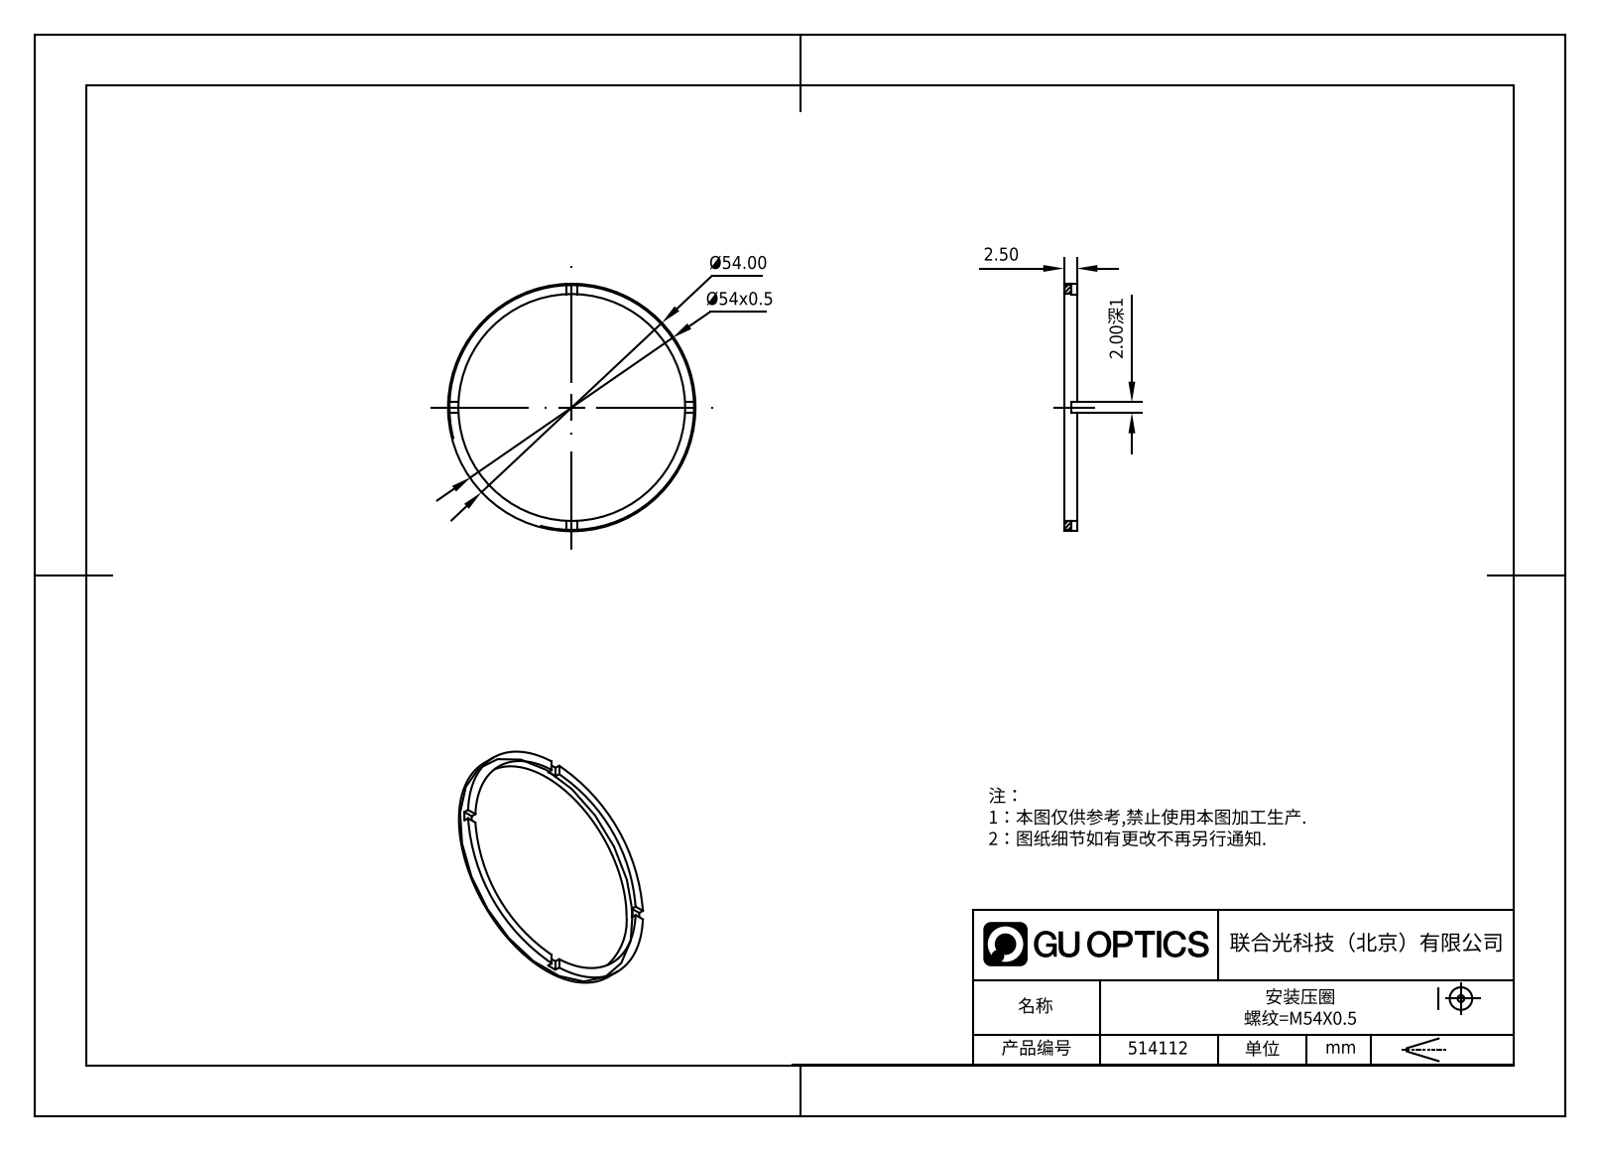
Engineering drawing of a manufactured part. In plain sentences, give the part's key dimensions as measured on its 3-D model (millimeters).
The part is named "514112". Its 3-D file was written by "SolidWorks 2020 (CONFIG_CONTROL_DESIGN)". It is 1 solid with 21 faces: 17 planar, 4 cylindrical and 0 other. Overall it measures 54 by 54 by 2.5 millimeters. Its volume is 991 cubic millimeters and its surface area 1 622 square millimeters. Round holes: 1 of diameter 49. Round bosses or shafts: 1 of diameter 54. The main face-to-face distances are 2.5, 1.5, 1, 2.
